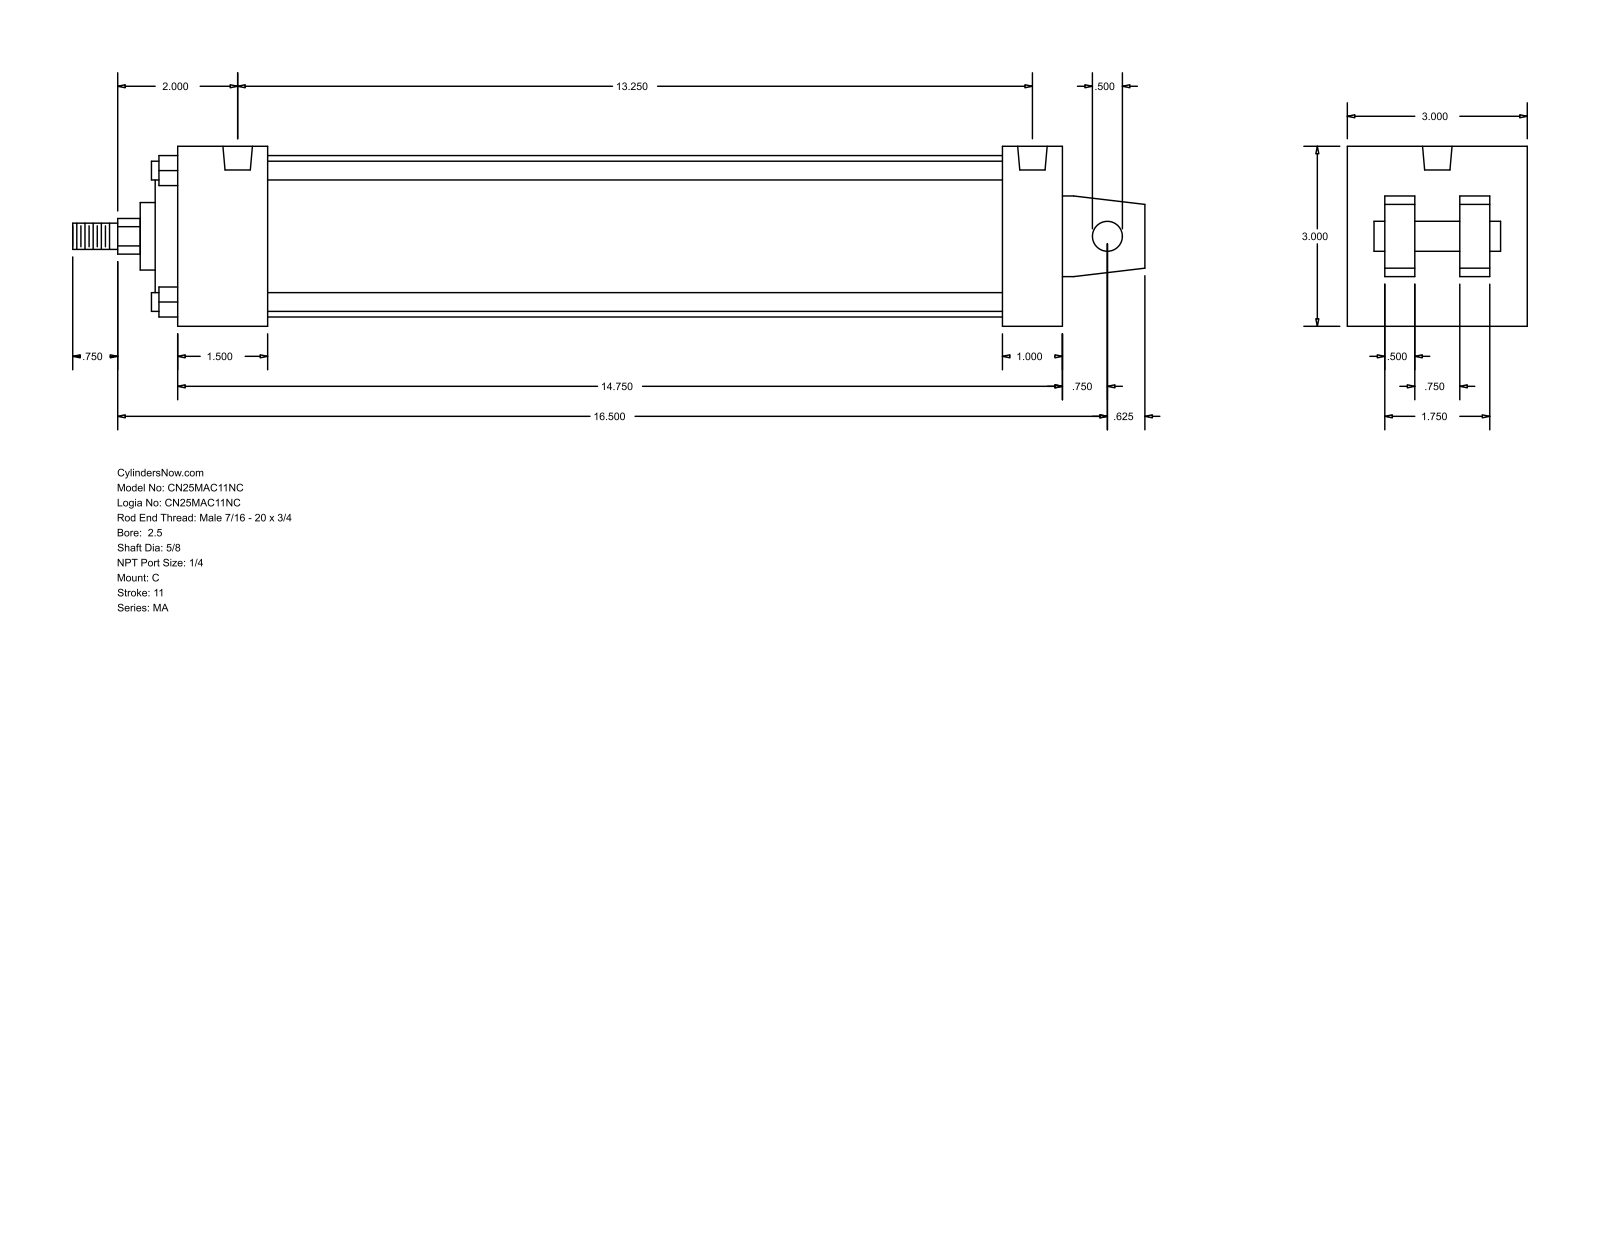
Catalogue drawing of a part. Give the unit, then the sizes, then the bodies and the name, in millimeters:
Units: millimetres
Overall size (bounding box): 454.02 × 76.2 × 76.2
Round holes (diameter × count): ⌀7.94 ×4, ⌀12.49 ×2
Round bosses / shafts (diameter × count): ⌀7.94 ×4, ⌀68.33 ×1, ⌀50.8 ×1, ⌀28.57 ×1, ⌀15.88 ×1, ⌀12.7 ×1, ⌀11.11 ×1
Partial cylindrical surfaces — rounded edges, fillets, slot ends (radius × count): R7.54 ×1
Main face-to-face distances: 76.2, 374.65, 12.7, 15.87, 60.33, 47.63, 25.4, 38.1, 349.25, 311.15
Hole centre spacings: 336.55
Bodies: 0 solids, 105 faces (77 planar, 28 cylindrical, 0 other)
Part name (STEP PRODUCT): MA_C__0250_0.625
STEP written by: GSSL Pune (CONFIG_CONTROL_DESIGN)
